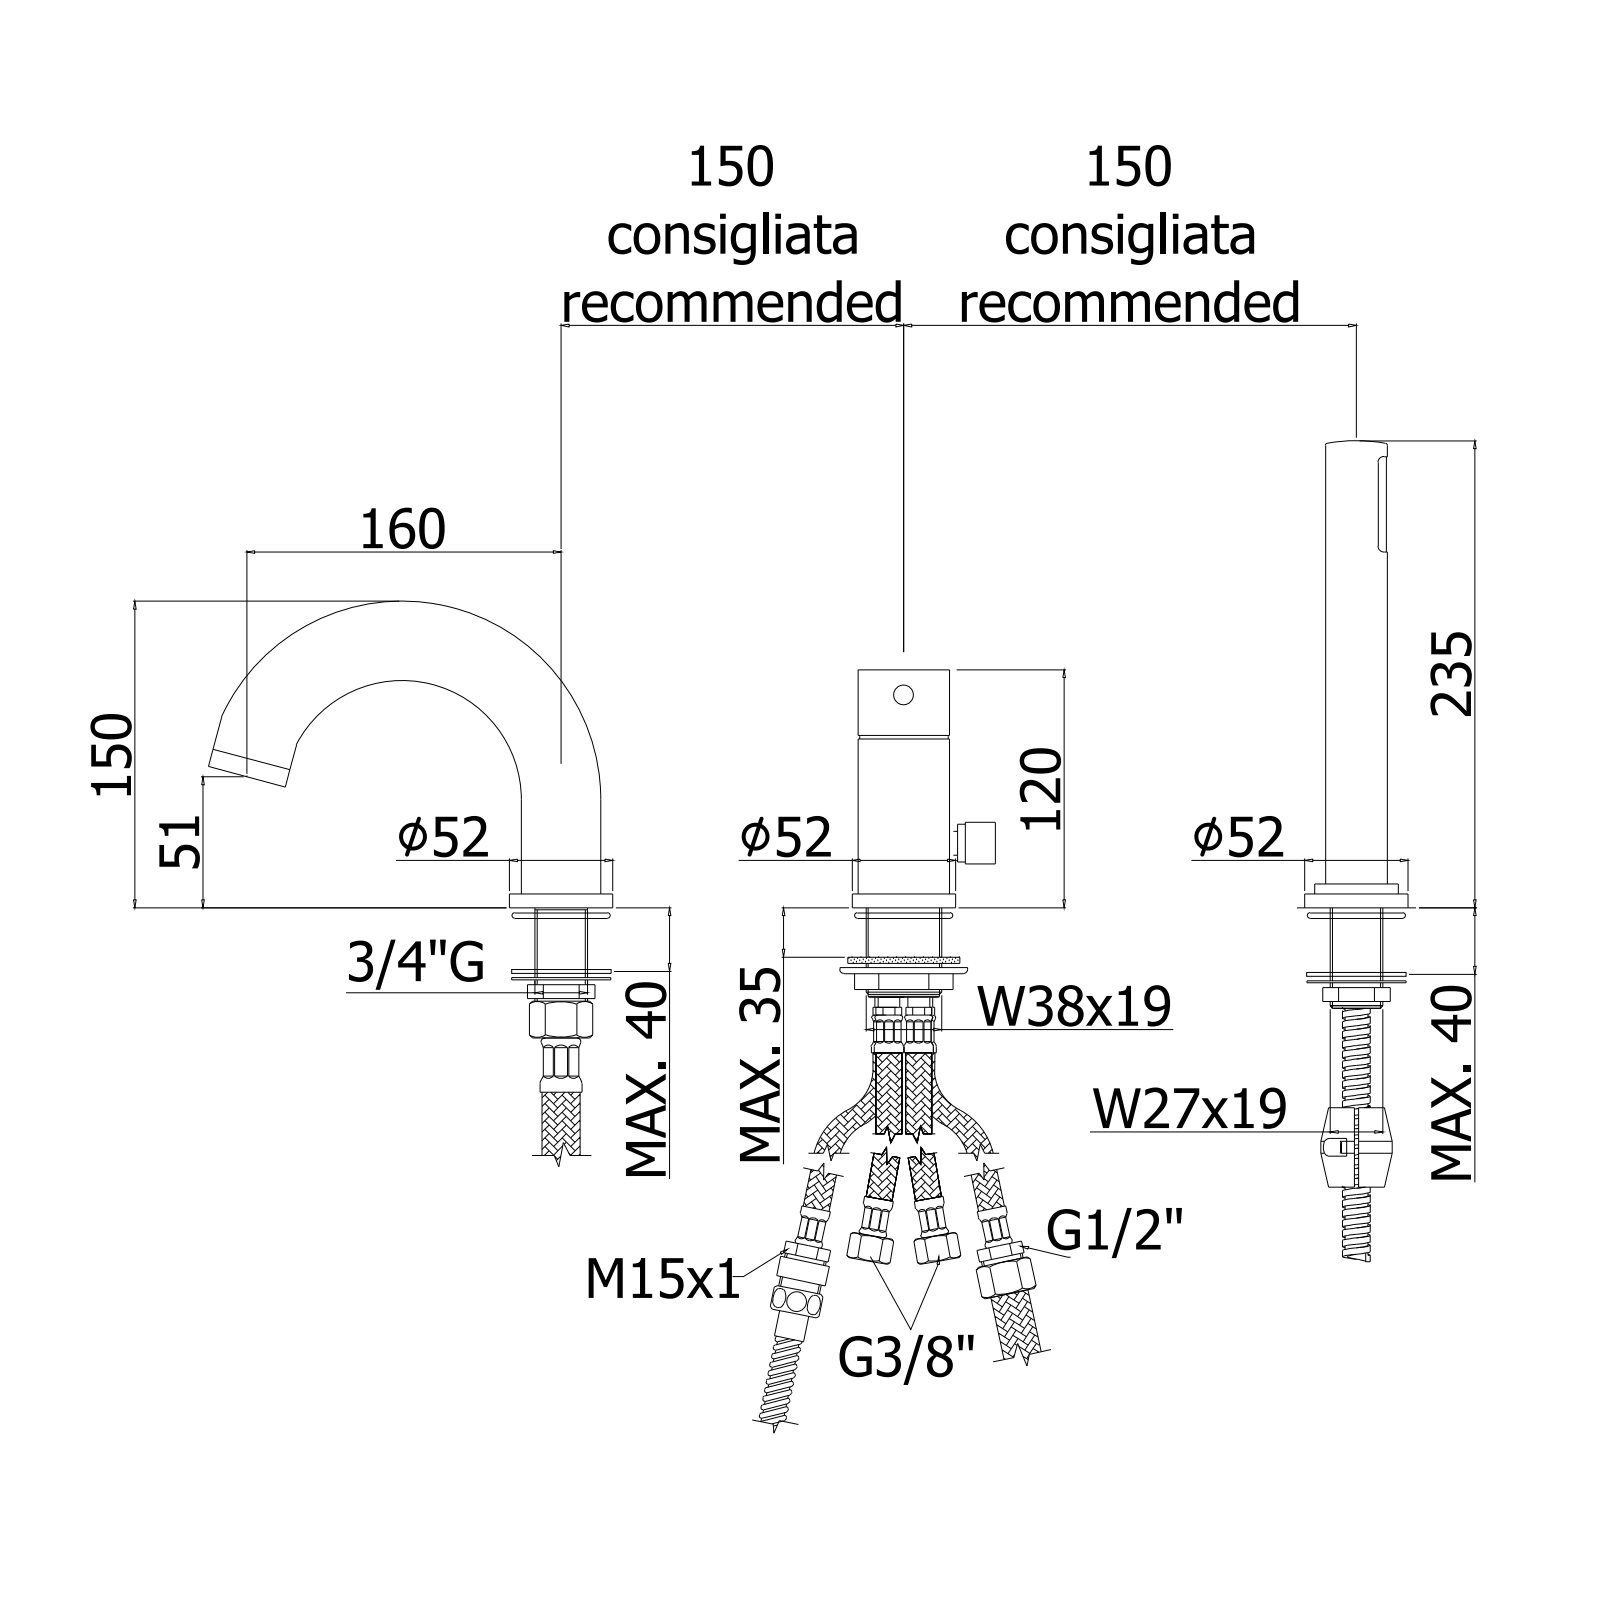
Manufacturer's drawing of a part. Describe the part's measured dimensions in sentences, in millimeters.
The part is named "LIG040L". Its 3-D file was written by "CREO PARAMETRIC BY PTC INC, 2020044 (CONFIG_CONTROL_DESIGN)". It is 0 solids with 572 faces: 247 planar, 236 cylindrical and 89 other. Overall it measures 352 by 222 by 205.82 millimeters. Round holes: 11 of diameter 1.5, 6 of diameter 0.5, 6 of diameter 7, 3 of diameter 49.2, 2 of diameter 26.8, 2 of diameter 33, 1 of diameter 3.3, 1 of diameter 4, 1 of diameter 4.2, 1 of diameter 6, 1 of diameter 7.2, 1 of diameter 9. Round bosses or shafts: 3 of diameter 52, 3 of diameter 44.2, 3 of diameter 36, 1 of diameter 46.5, 1 of diameter 42, 1 of diameter 32, 1 of diameter 23.5, 1 of diameter 23.4. Partial cylindrical surfaces (rounded edges, fillets, slot ends): 35 of radius 0.25, 5 of radius 0.75, 4 of radius 0.5, 2 of radius 0.3, 2 of radius 1, 2 of radius 7.8, 2 of radius 9.8, 2 of radius 10. The main face-to-face distances are 7, 5, 10, 2, 12, 220, 10.5, 1.5, 15, 115.7. The hole center spacings are 7.64, 6.5, 7.91, 14.98, 5.73, 13.5, 19.14, 4.5.
